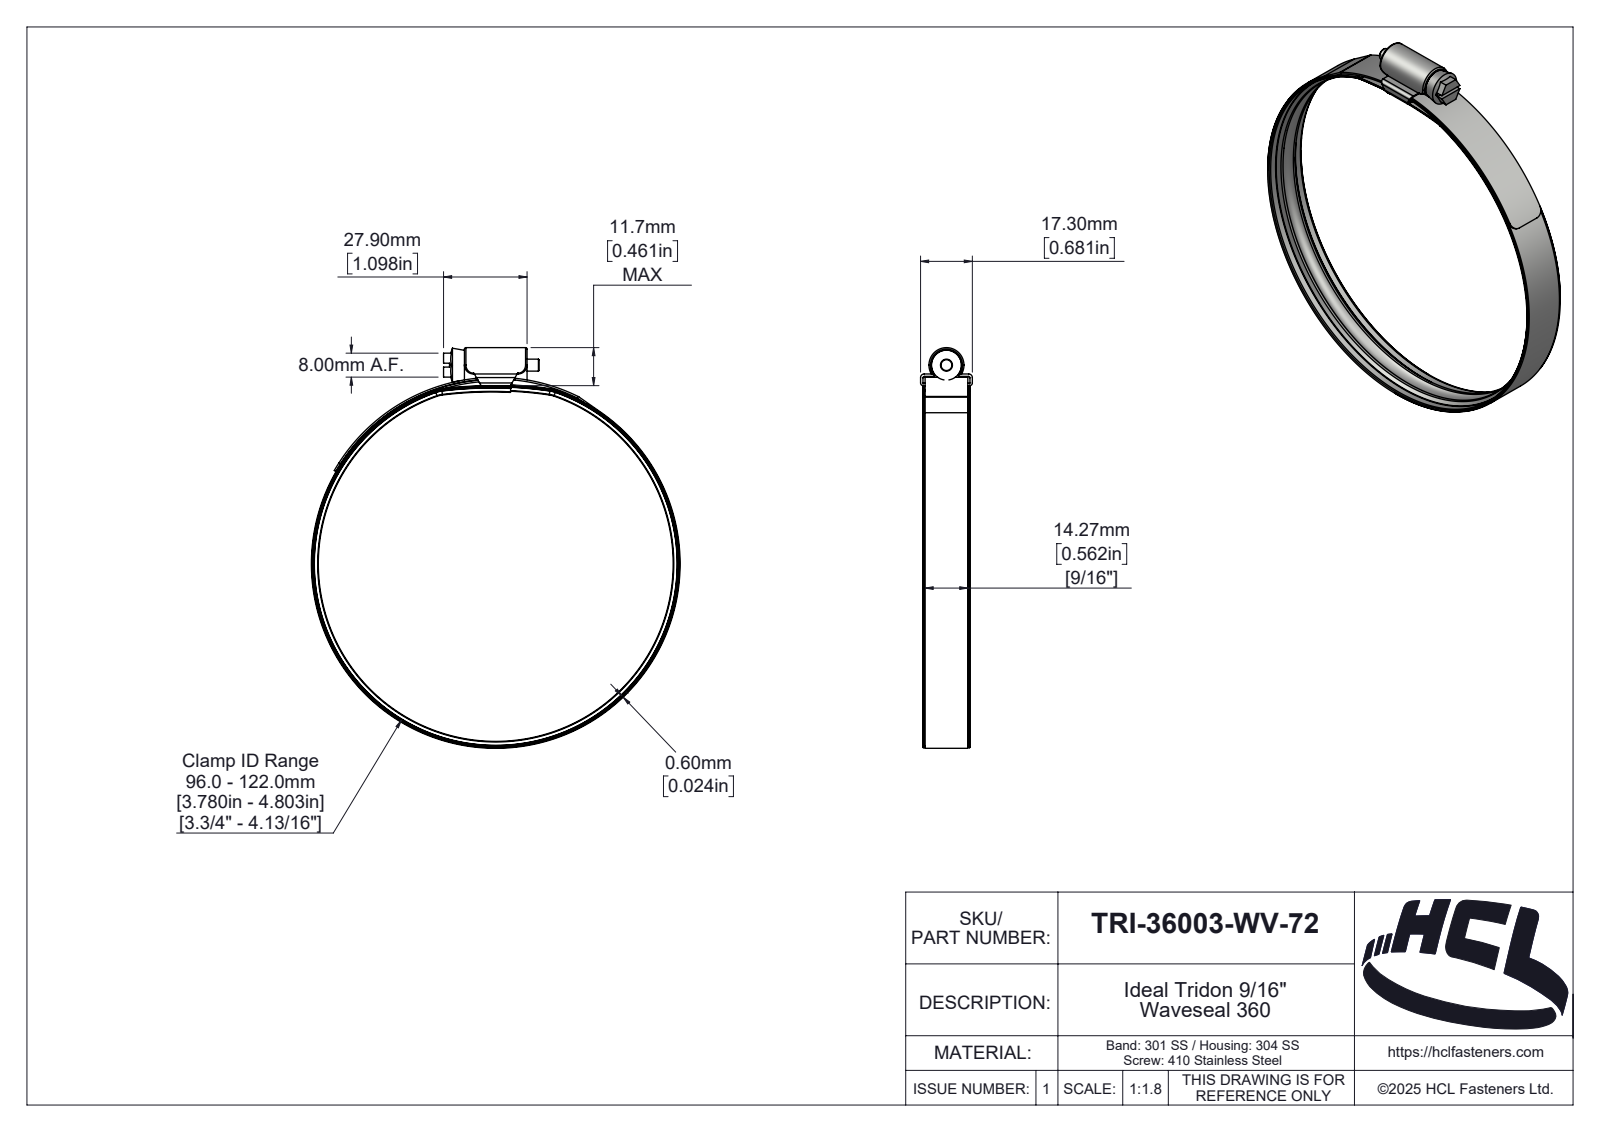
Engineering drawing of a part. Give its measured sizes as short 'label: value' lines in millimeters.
name: TRI-36003-WV-72
written by: SolidWorks 2025 (AUTOMOTIVE_DESIGN)
unit: mm
bodies: 4 solids, 418 faces (42 planar, 119 cylindrical, 257 other)
size: 133.8 × 123.2 × 17.3
volume: 8 075 mm³; area: 30 068 mm²
holes: 1× ⌀121.4, 1× ⌀122
bosses: 1× ⌀123.2, 1× ⌀121.8, 1× ⌀10, 1× ⌀4
rounds: 6× R0.5, 4× R3, 2× R0.1, 2× R0.9, 2× R1.2, 2× R9.9, 2× R10.1, 1× R0.46
face distances: 14.26, 0.8, 3.1, 0.6, 2.3, 3.9, 27.9, 1.52, 15.78, 16.5
